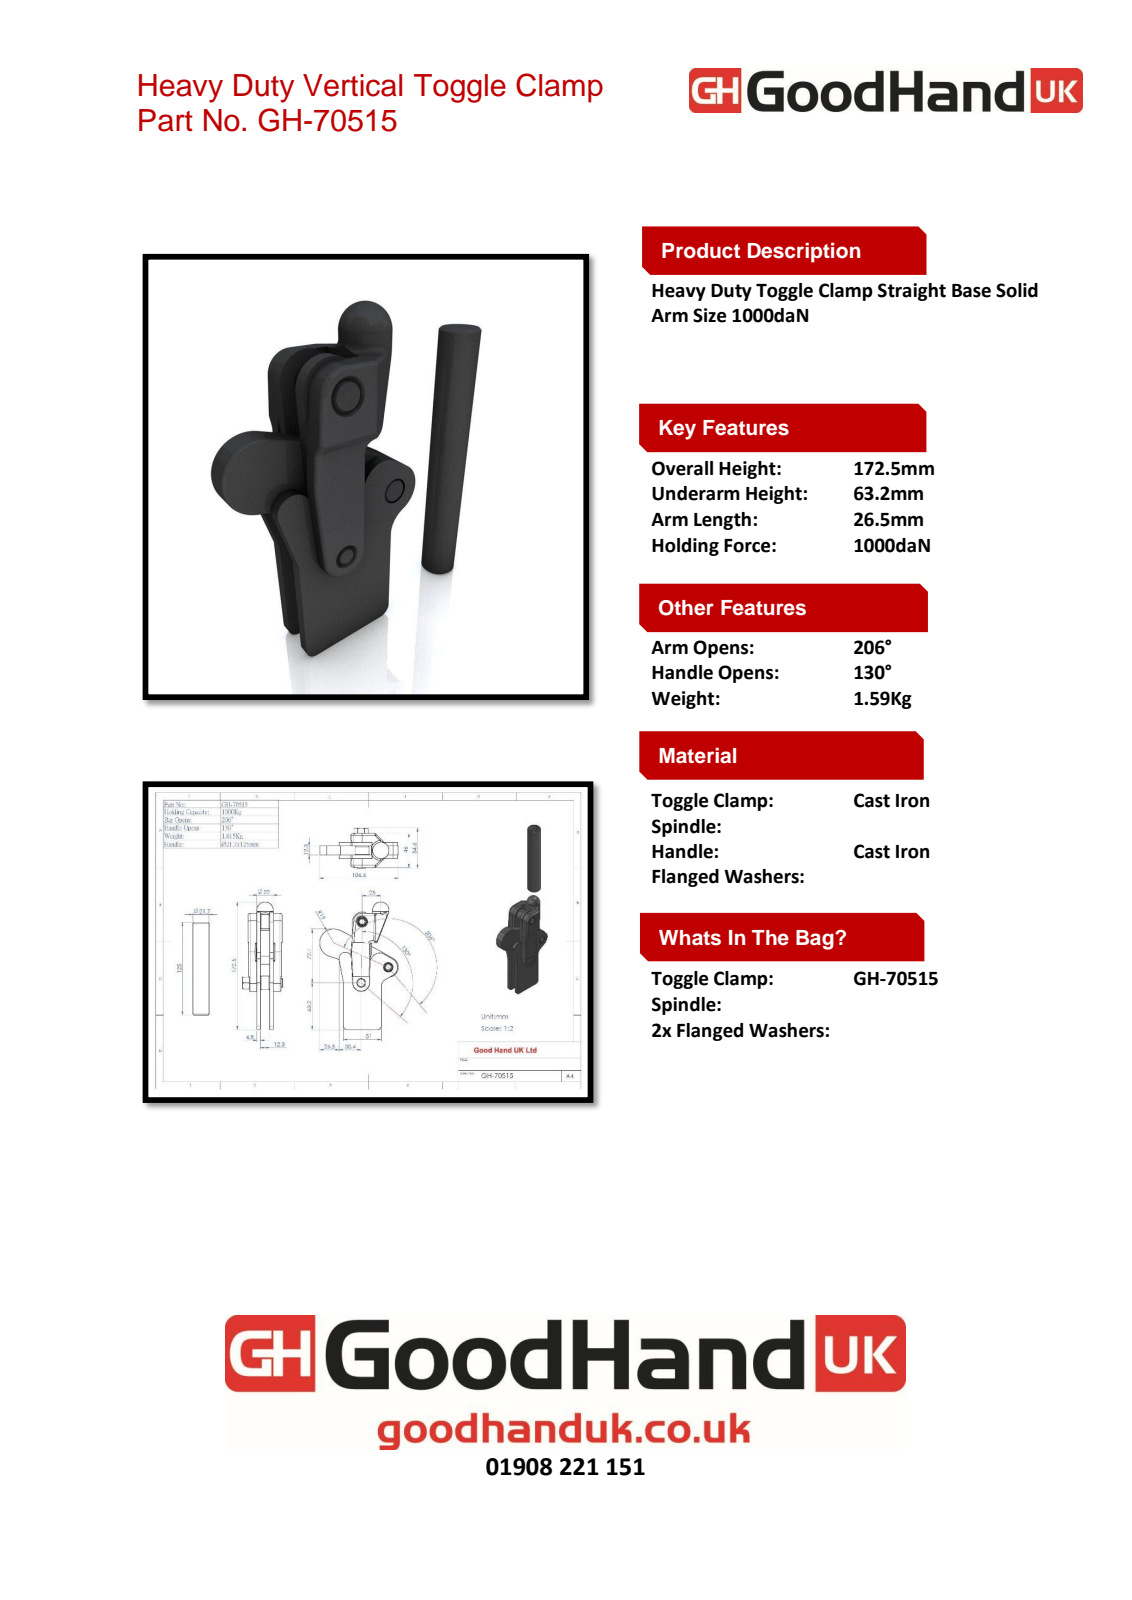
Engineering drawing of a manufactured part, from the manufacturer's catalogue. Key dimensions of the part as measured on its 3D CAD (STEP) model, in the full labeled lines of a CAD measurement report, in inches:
Part name (STEP PRODUCT): Group5^GH-70515(簡化)-1; 3700808-1^GH-70515(簡化)-1; Group1^GH-70515(簡化)-1; 17030501-1^GH-70515(簡化)-1 (+2 more)
STEP written by: SolidWorks 2016 (AUTOMOTIVE_DESIGN)
Units: inches
Bodies: 5 solids, 164 faces (68 planar, 71 cylindrical, 25 other)
Overall size (bounding box): 11.712 × 4.176 × 2.15
Volume: 13.39 in³ · Surface area: 128.1 in²
Round holes (diameter × count): ⌀0.374 ×4, ⌀0.394 ×1, ⌀0.677 ×1
Round bosses / shafts (diameter × count): ⌀0.865 ×1, ⌀0.854 ×1, ⌀0.748 ×1, ⌀0.472 ×1
Partial cylindrical surfaces — rounded edges, fillets, slot ends (radius × count): R0.079 ×2, R0.197 ×2, R0.453 ×2, R0.512 ×2, R0.331 ×1, R0.335 ×1, R0.394 ×1, R0.437 ×1
Main face-to-face distances: 0.191, 0.675, 0.484, 0.68, 0.866, 0.196, 0.871, 0.876, 0.871, 0.68
Hole centre spacings: 1.603, 1.618, 1.634, 1.661, 2.791, 3.252
